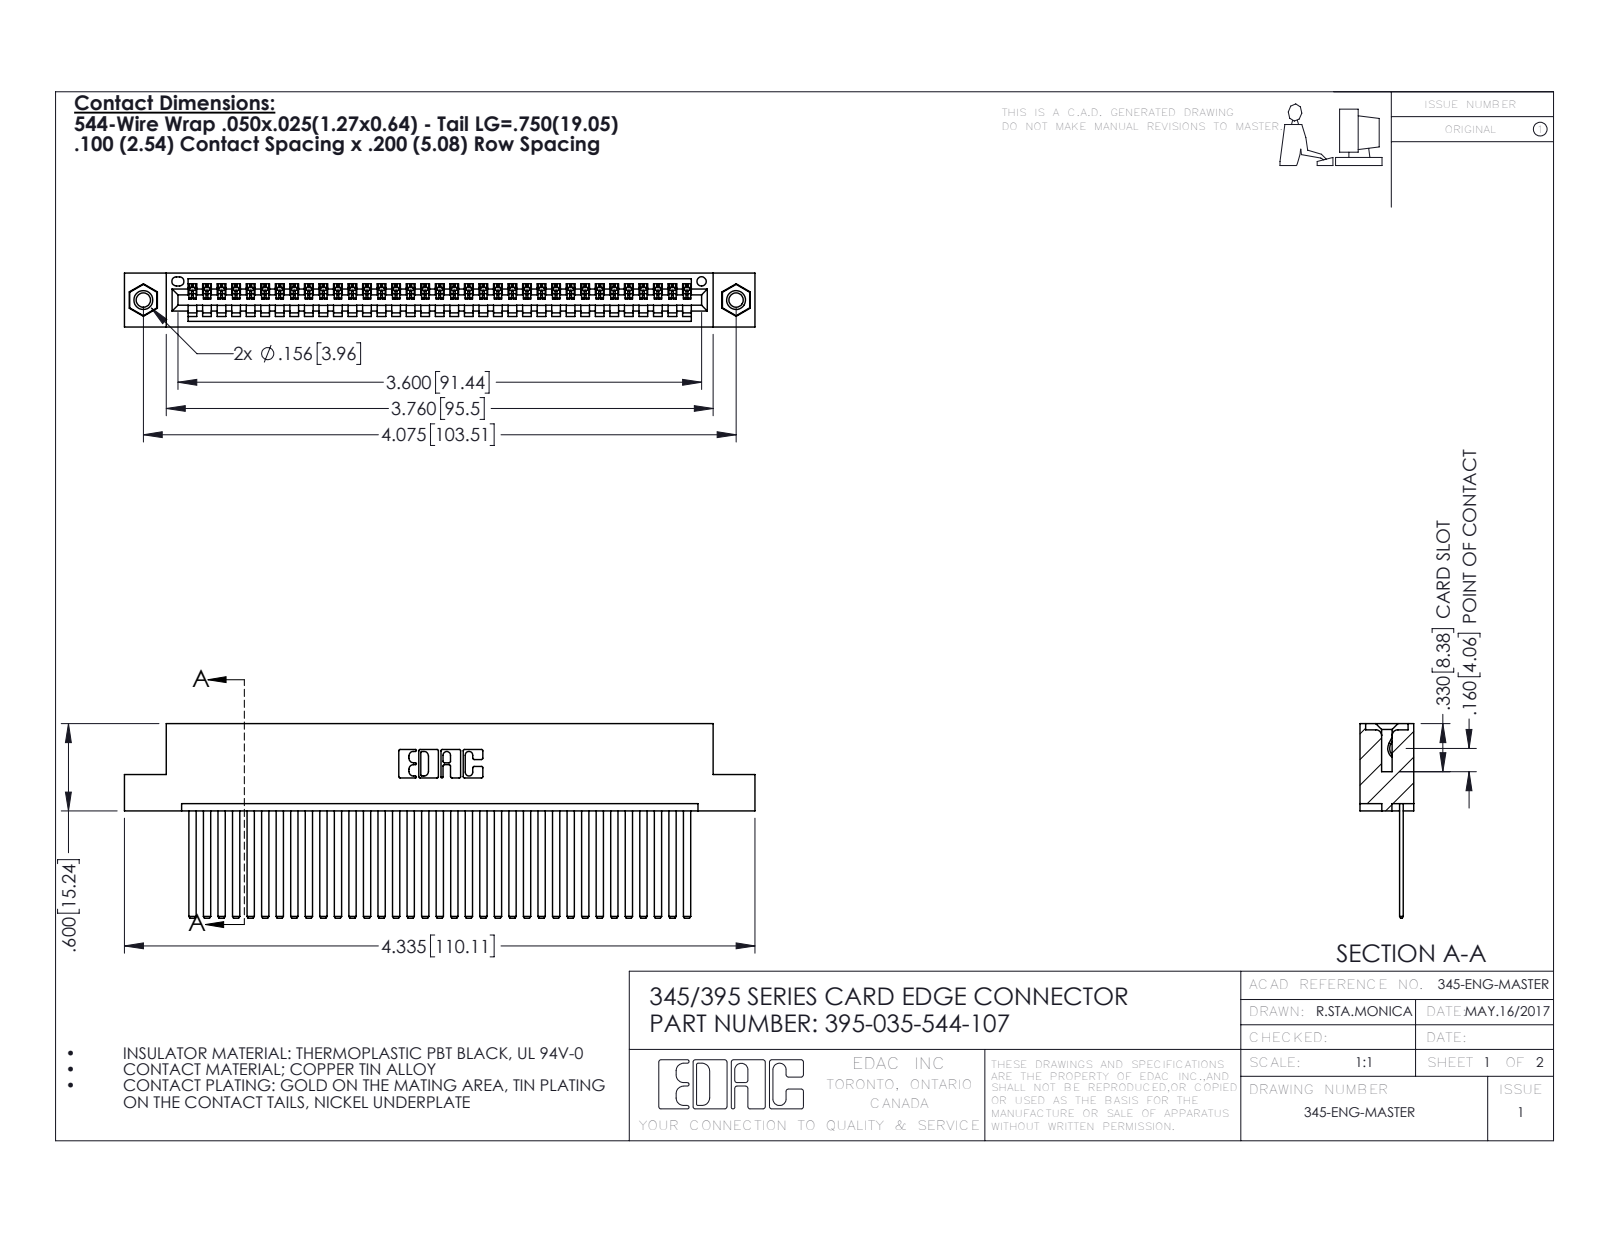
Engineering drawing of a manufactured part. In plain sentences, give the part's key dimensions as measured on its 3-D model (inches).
The part is named "345-292-001_345-293-144; 345 Part_Flush Mounting Lugs - 0.156 Dia-TI; 345-250-001_345-250-005-103; 395-035-544-107". Its 3-D file was written by "SolidWorks 2016 (CONFIG_CONTROL_DESIGN)". It is 38 solids with 2006 faces: 1372 planar, 618 cylindrical and 16 other. Overall it measures 4.335 by 1.337 by 0.37 inches. Its volume is 0.659 cubic inches and its surface area 24.02 square inches. Round holes: 2 of diameter 0.098, 2 of diameter 0.125, 2 of diameter 0.156, 1 of diameter 0.064. Round bosses or shafts: 2 of diameter 0.155. Partial cylindrical surfaces (rounded edges, fillets, slot ends): 70 of radius 0.006, 22 of radius 0.01, 6 of radius 0.007, 6 of radius 0.031, 3 of radius 0.026, 2 of radius 0.031, 2 of radius 0.04, 1 of radius 0.014. The main face-to-face distances are 0.072, 0.298, 0.025, 0.098, 0.272, 0.37, 0.2, 0.225, 0.149, 0.072. The hole center spacings are 0.27, 3.839, 4.075.
